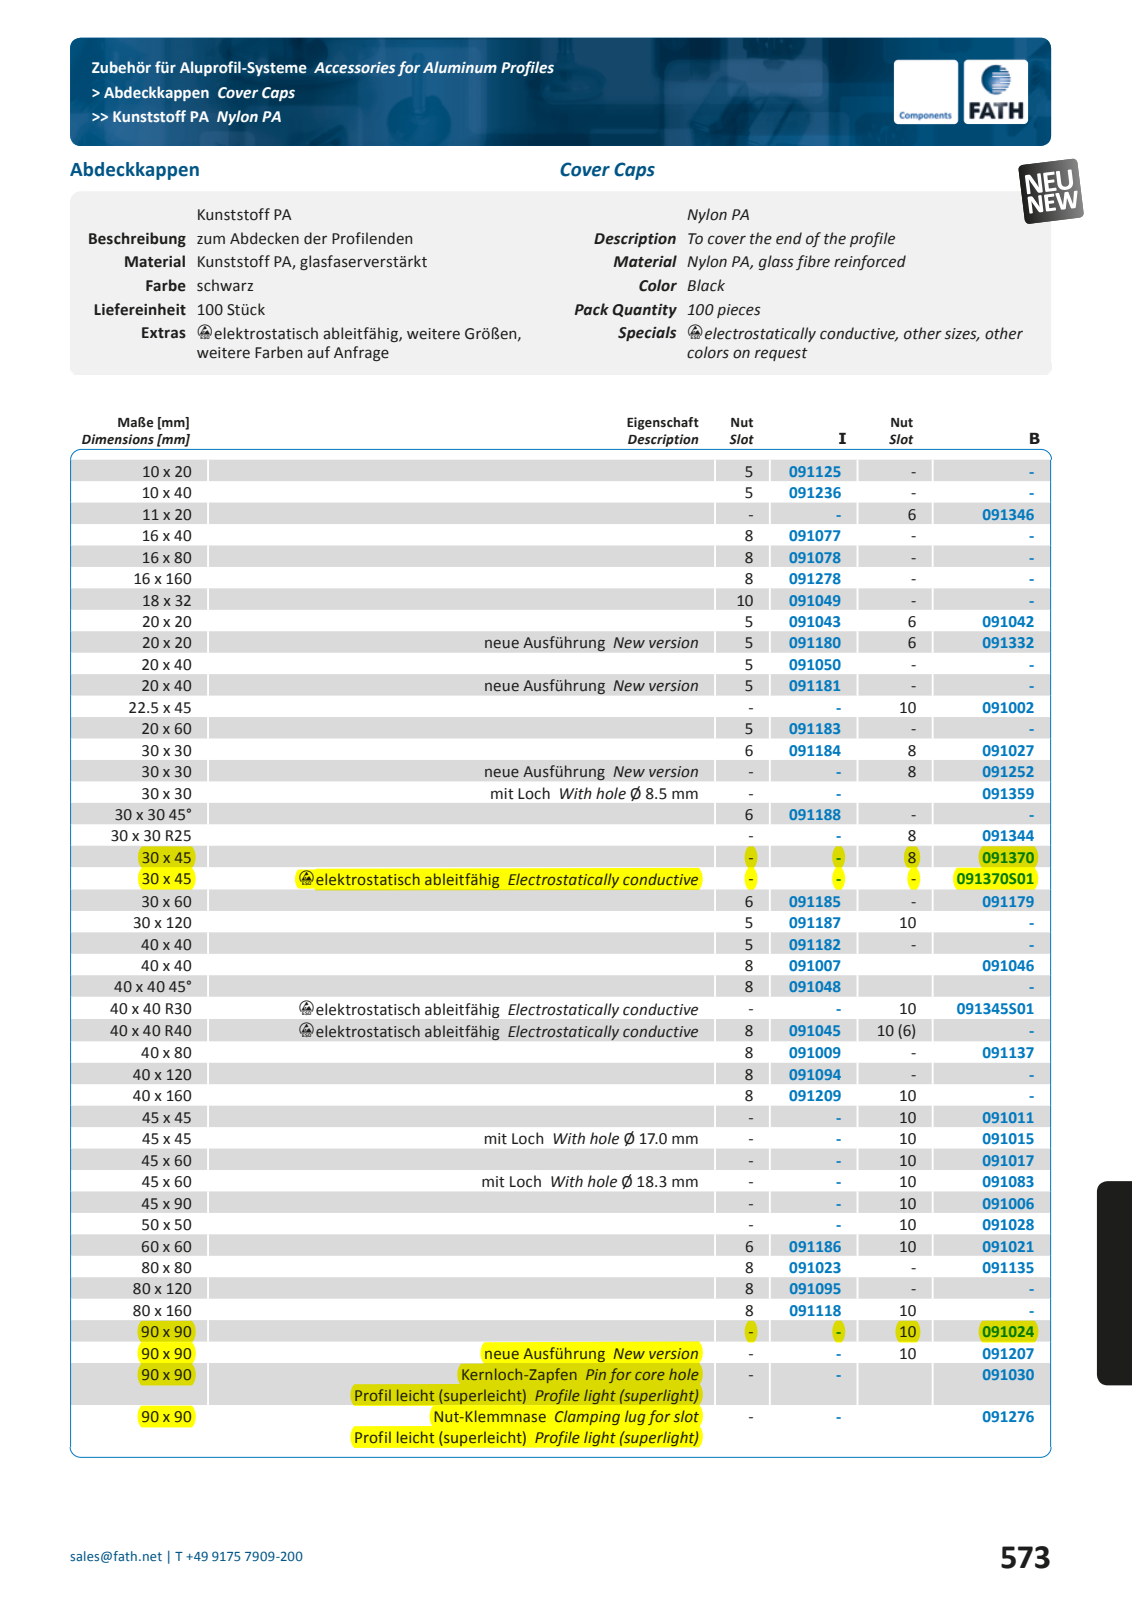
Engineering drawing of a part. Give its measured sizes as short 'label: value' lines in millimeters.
name: fath_091077
written by: Spatial InterOp 3D (automotive_design)
unit: mm
bodies: 1 solid, 143 faces (47 planar, 68 cylindrical, 28 other)
size: 40 × 16 × 9.5
volume: 1 765 mm³; area: 2 128 mm²
holes: 2× ⌀2.4
rounds: 36× R0.2, 4× R2, 4× R3.5, 2× R2.55
face distances: 2, 4, 14, 16, 12, 3.37, 38, 36, 40, 27.05
hole spacings: 28
